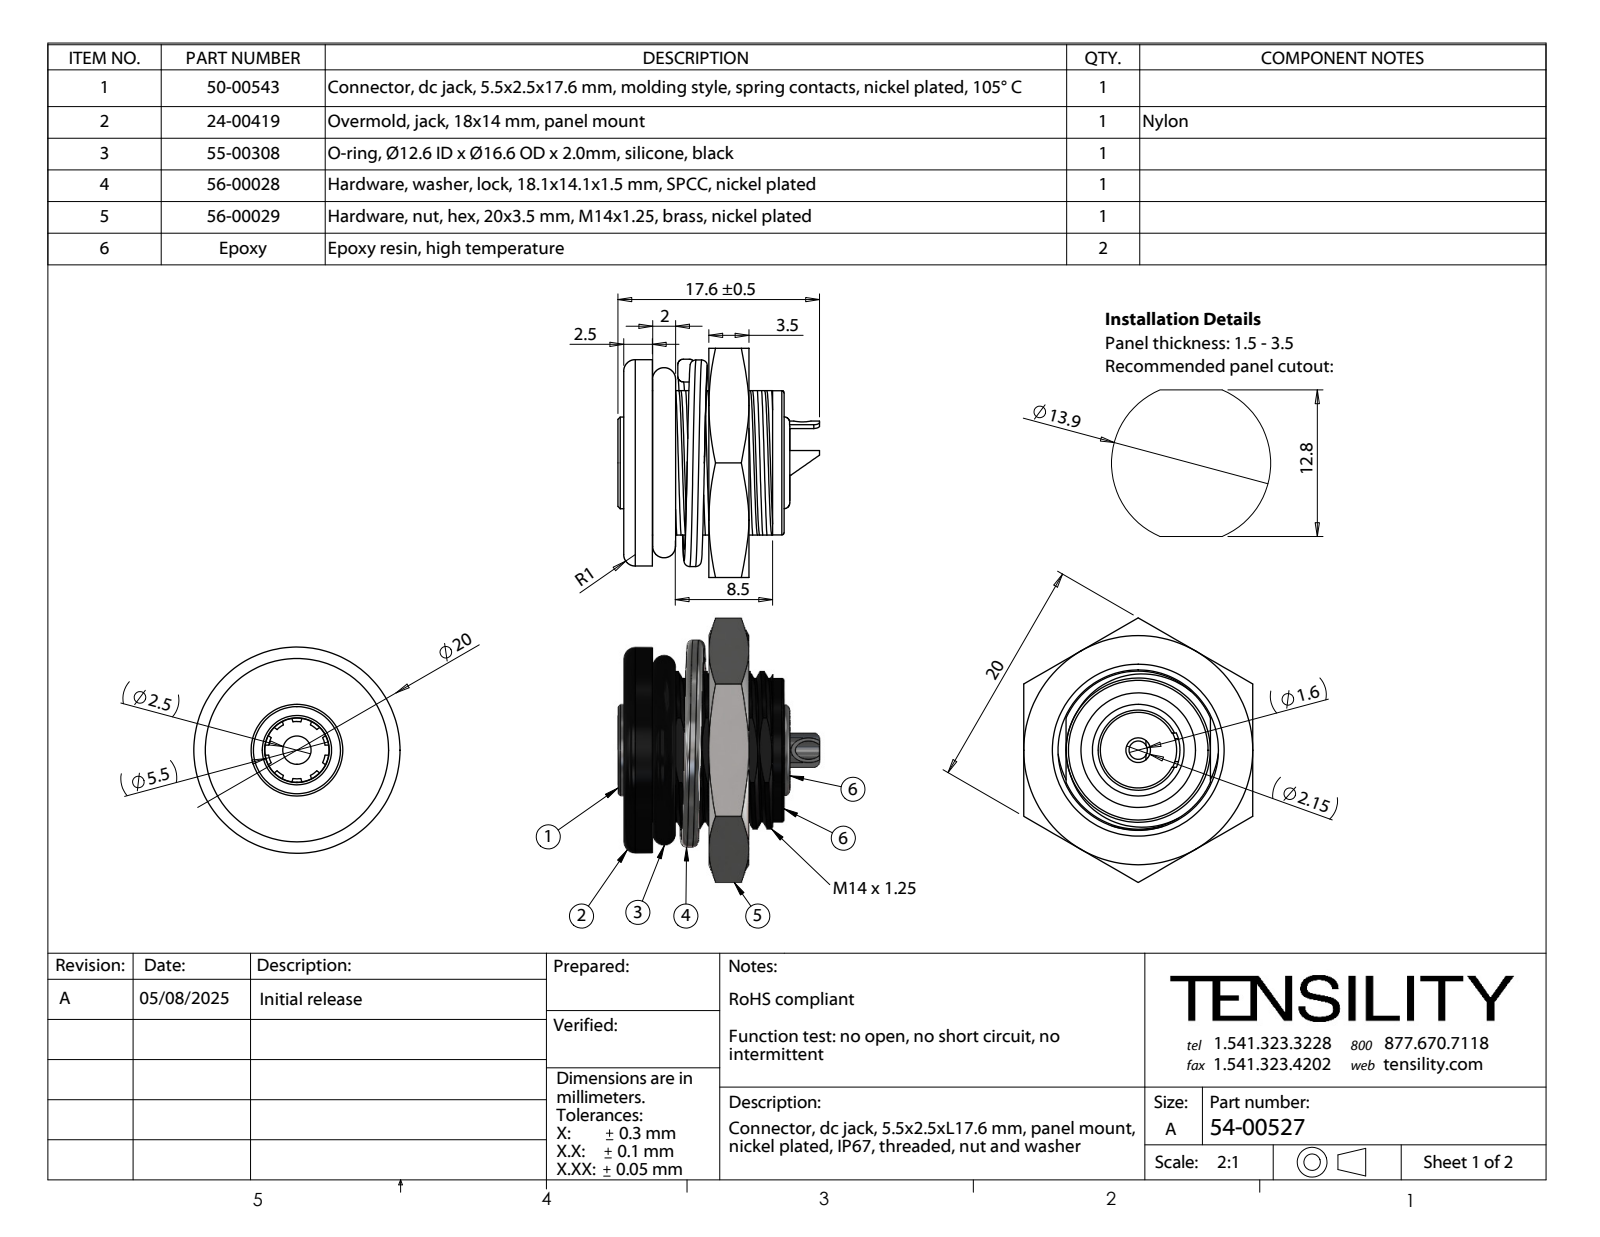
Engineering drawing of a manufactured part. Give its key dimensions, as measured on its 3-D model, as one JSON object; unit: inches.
{"part_name": "55-00308; 50-00543 shell_Shell; 50-00543 center pin_Center pin; 50-00543 spring contact_Terminal (+6 more)", "step_written_by": "SolidWorks 2021 (CONFIG_CONTROL_DESIGN)", "units": "inches", "bodies": {"solids": 8, "faces": 286, "planar": 100, "cylindrical": 79, "other": 107}, "overall_size": [0.909, 0.787, 0.693], "volume_in3": 0.172, "surface_area_in2": 6.584, "round_holes": [[0.059, 2], [0.063, 1], [0.085, 1], [0.097, 1], [0.22, 1], [0.222, 1], [0.252, 1], [0.26, 1], [0.299, 1], [0.315, 1], [0.394, 1], [0.551, 1]], "round_bosses_or_shafts": [[0.709, 1], [0.496, 1], [0.496, 1], [0.287, 1], [0.244, 1]], "partial_cylinders_radius": [[0.02, 2], [0.132, 1], [0.272, 1]], "face_to_face_distances": [0.138, 0.43, 0.293, 0.332, 0.194, 0.098, 0.787, 0.146, 0.642, 0.039]}
